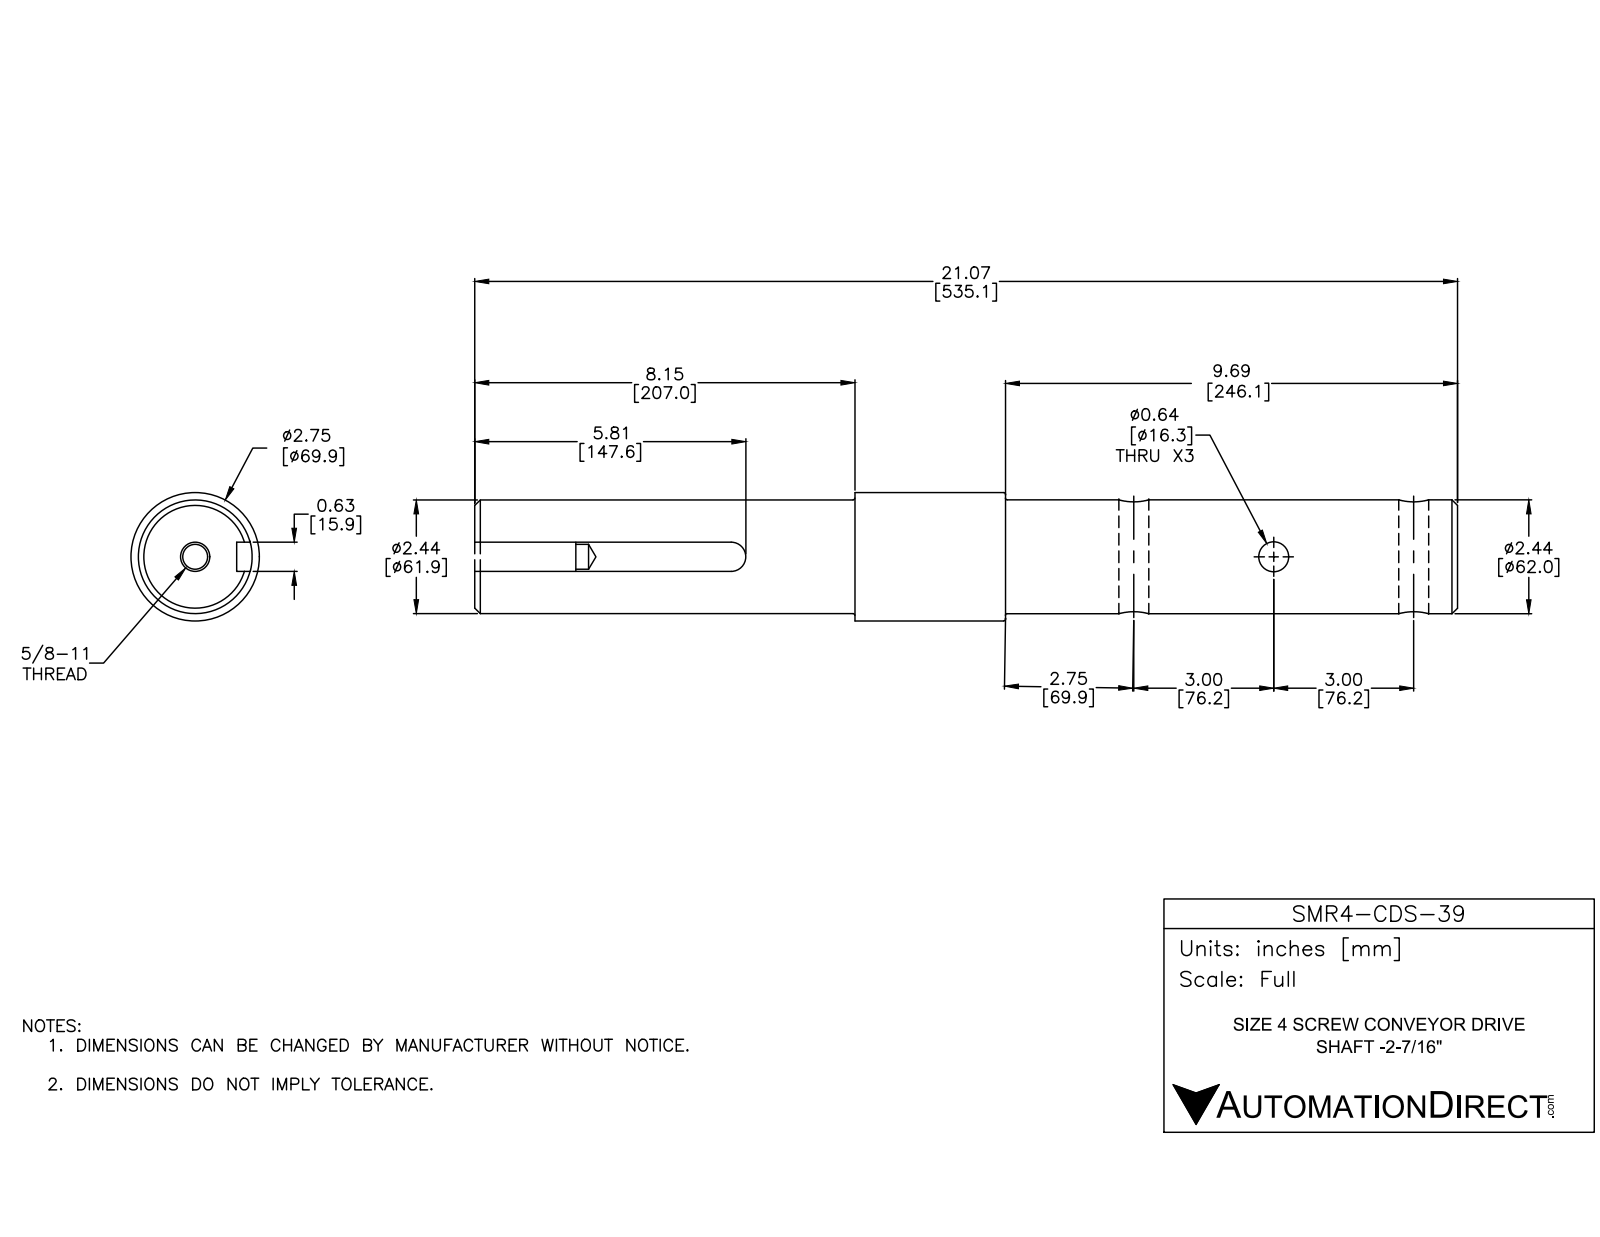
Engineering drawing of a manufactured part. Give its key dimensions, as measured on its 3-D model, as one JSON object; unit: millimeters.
{"part_name": "SMR4-CDS-39", "step_written_by": "SolidWorks 2016 (AUTOMOTIVE_DESIGN)", "units": "millimeters", "bodies": {"solids": 1, "faces": 38, "planar": 8, "cylindrical": 18, "other": 12}, "overall_size": [535.1, 69.9, 69.9], "volume_mm3": 1609000, "surface_area_mm2": 126100, "round_holes": [[16.3, 3], [13.5, 1], [15.9, 1]], "round_bosses_or_shafts": [[69.9, 1], [62, 1], [61.9, 1]], "partial_cylinders_radius": [[7.9, 1]], "face_to_face_distances": [535.1, 15.9, 207, 328.1, 289, 82, 246.1, 55, 152, 234], "hole_center_spacings": [152.4]}
